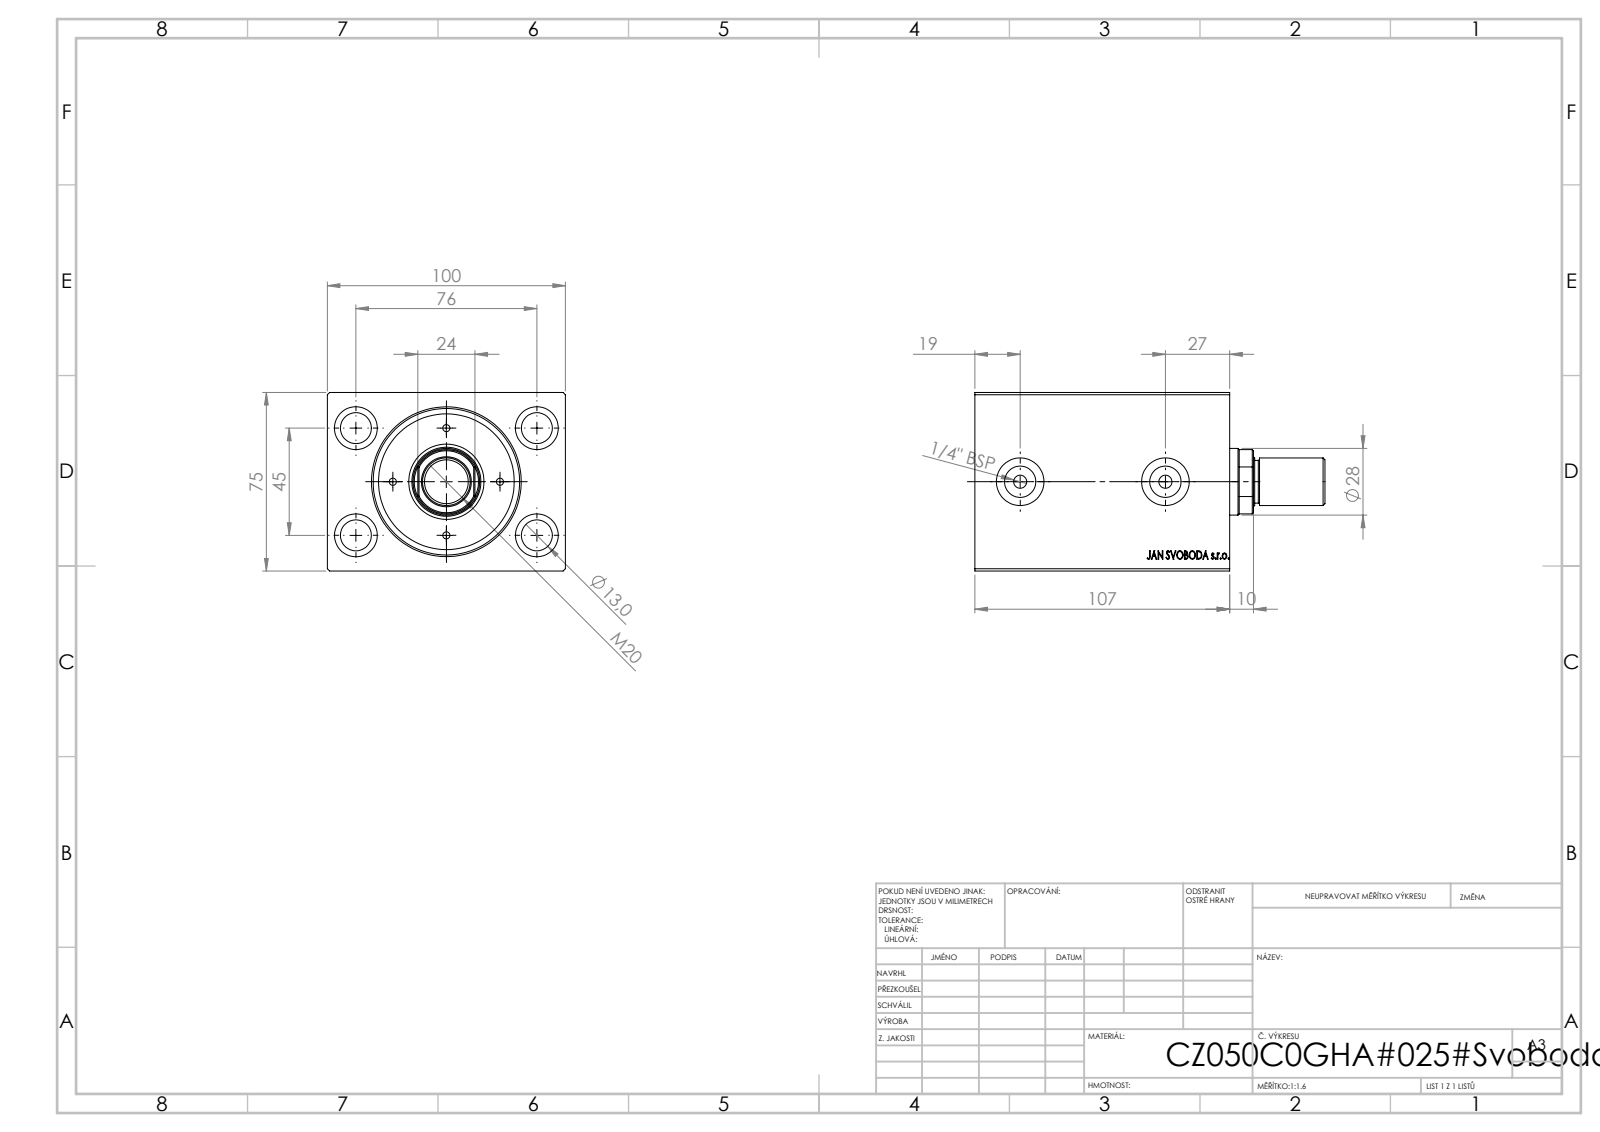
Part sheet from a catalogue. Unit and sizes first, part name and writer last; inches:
Units: inches
Overall size (bounding box): 4.213 × 3.937 × 2.953
Round holes (diameter × count): ⌀0.512 ×4, ⌀0.709 ×4, ⌀0.217 ×2, ⌀0.315 ×2, ⌀0.518 ×2, ⌀0.787 ×2, ⌀1.417 ×1, ⌀1.969 ×1, ⌀2.421 ×1
Main face-to-face distances: 2.953, 3.937, 4.213, 3.512, 0.701, 4.205, 0.693, 0.394, 3.118, 3.811
Hole centre spacings: 1.739, 1.772, 2.992, 3.477, 1.614, 2.402
Volume: 33.3 in³ · Surface area: 133 in²
Bodies: 1 solid, 825 faces (397 planar, 46 cylindrical, 382 other)
STEP written by: SolidWorks 2019 (CONFIG_CONTROL_DESIGN)
